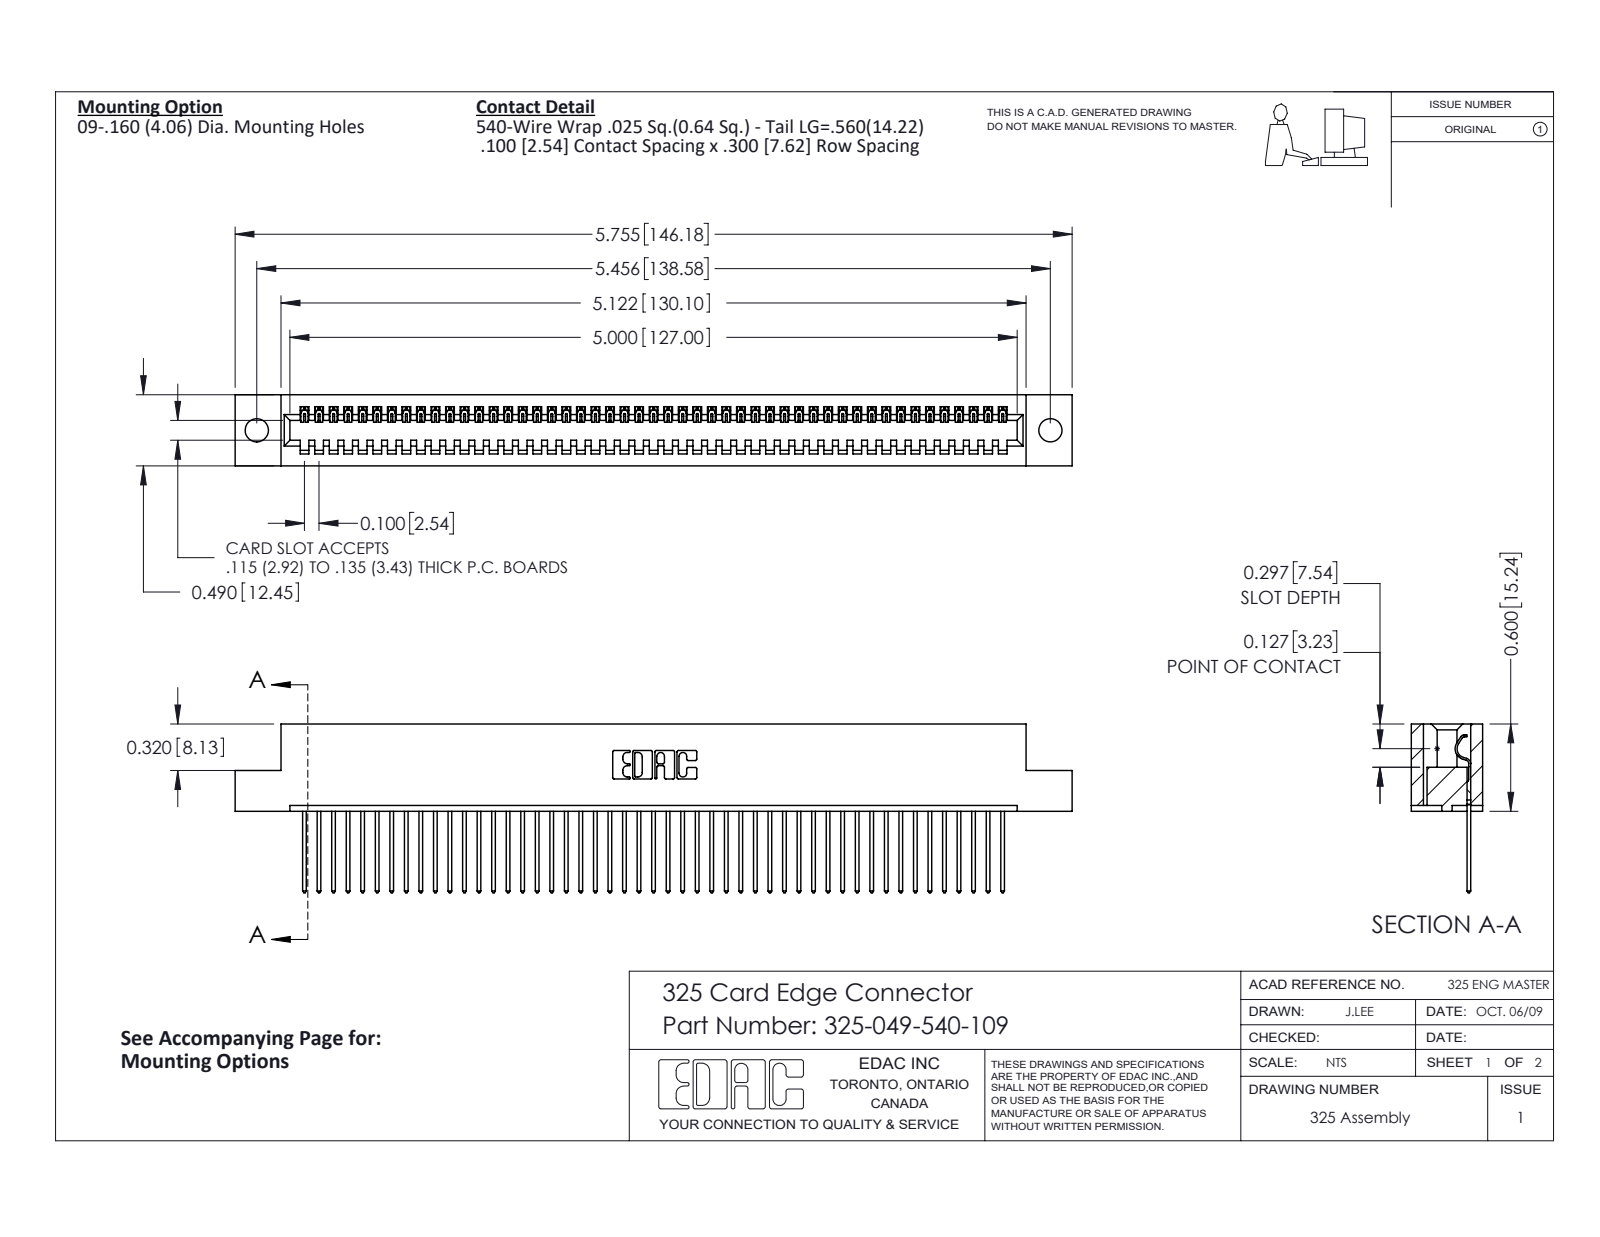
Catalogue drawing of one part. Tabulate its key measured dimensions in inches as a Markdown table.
| quantity | value |
| --- | --- |
| part name | 325-049-540-109; 325 Part_.160 TH; 325-292-001_325-293-140 |
| STEP written by | SolidWorks 2016 (CONFIG_CONTROL_DESIGN) |
| units | inches |
| bodies | 50 solids, 2956 faces (2128 planar, 828 cylindrical, 0 other) |
| overall size | 5.755 × 1.16 × 0.49 |
| volume | 1.126 in³ |
| surface area | 32.02 in² |
| round holes (diameter × count) | 0.16 × 2 |
| partial cylindrical surfaces (radius × count) | 0.006 × 98, 0.01 × 98, 0.01 × 22, 0.007 × 6, 0.031 × 6, 0.026 × 3, 0.014 × 1, 0.022 × 1 |
| main face-to-face distances | 0.083, 0.407, 0.49, 0.3, 0.107, 0.383, 0.025, 0.325, 0.56, 0.263 |
| hole center spacings | 5.456 |
